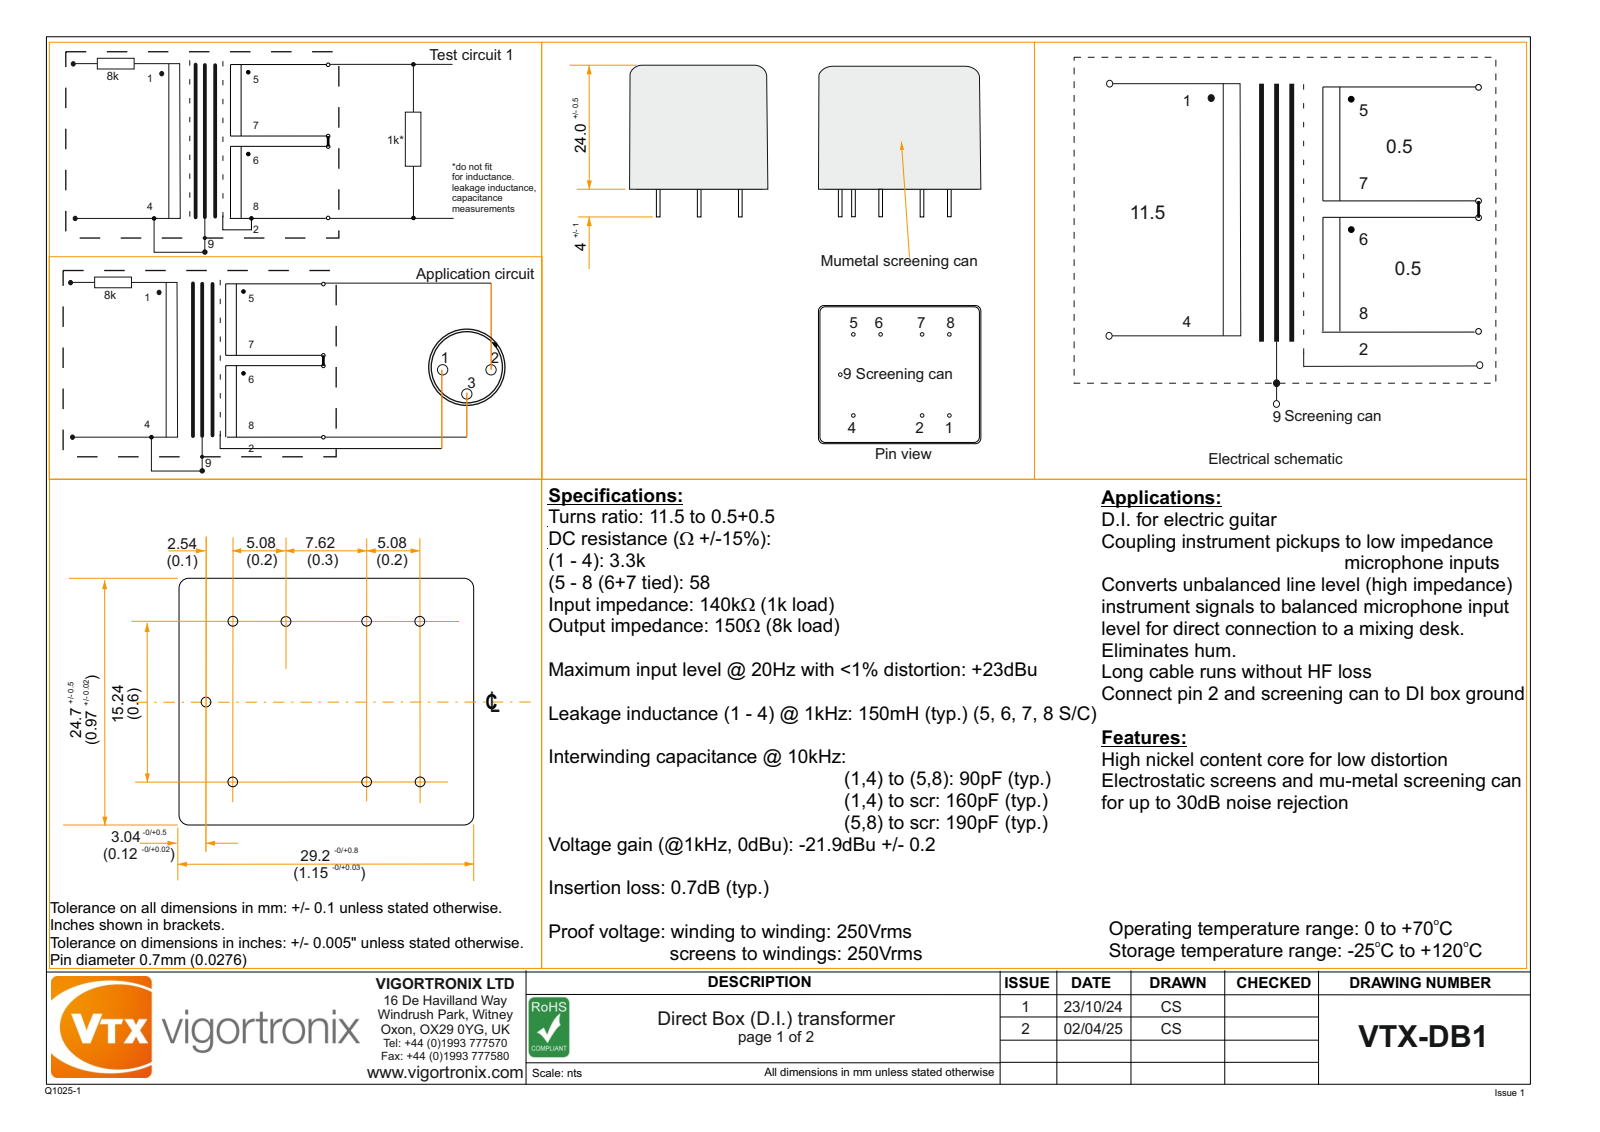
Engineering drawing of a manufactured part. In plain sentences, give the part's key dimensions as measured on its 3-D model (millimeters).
The part is named "VTX-DB1 BOBBIN; VTX-DB1 LID; VTX-DB1 CAN; VTX-DB1". Its 3-D file was written by "SolidWorks 2024 (AUTOMOTIVE_DESIGN)". It is 3 solids with 130 faces: 36 planar, 74 cylindrical and 20 other. Overall it measures 29.62 by 28.6 by 25.22 millimeters. Its volume is 15 314 cubic millimeters and its surface area 10 856 square millimeters. Round holes: 8 of diameter 3.5, 1 of diameter 1.5. Round bosses or shafts: 8 of diameter 0.7. Partial cylindrical surfaces (rounded edges, fillets, slot ends): 20 of radius 0.5, 8 of radius 1.9, 8 of radius 2.5, 4 of radius 2. The main face-to-face distances are 0.6, 23.4, 22.8, 22.5, 0.9, 23.1, 24, 23, 27.5, 2.6. The hole center spacings are 5.08, 12.7, 15.24, 16.06, 17.04, 19.84, 7.62, 8.03.
